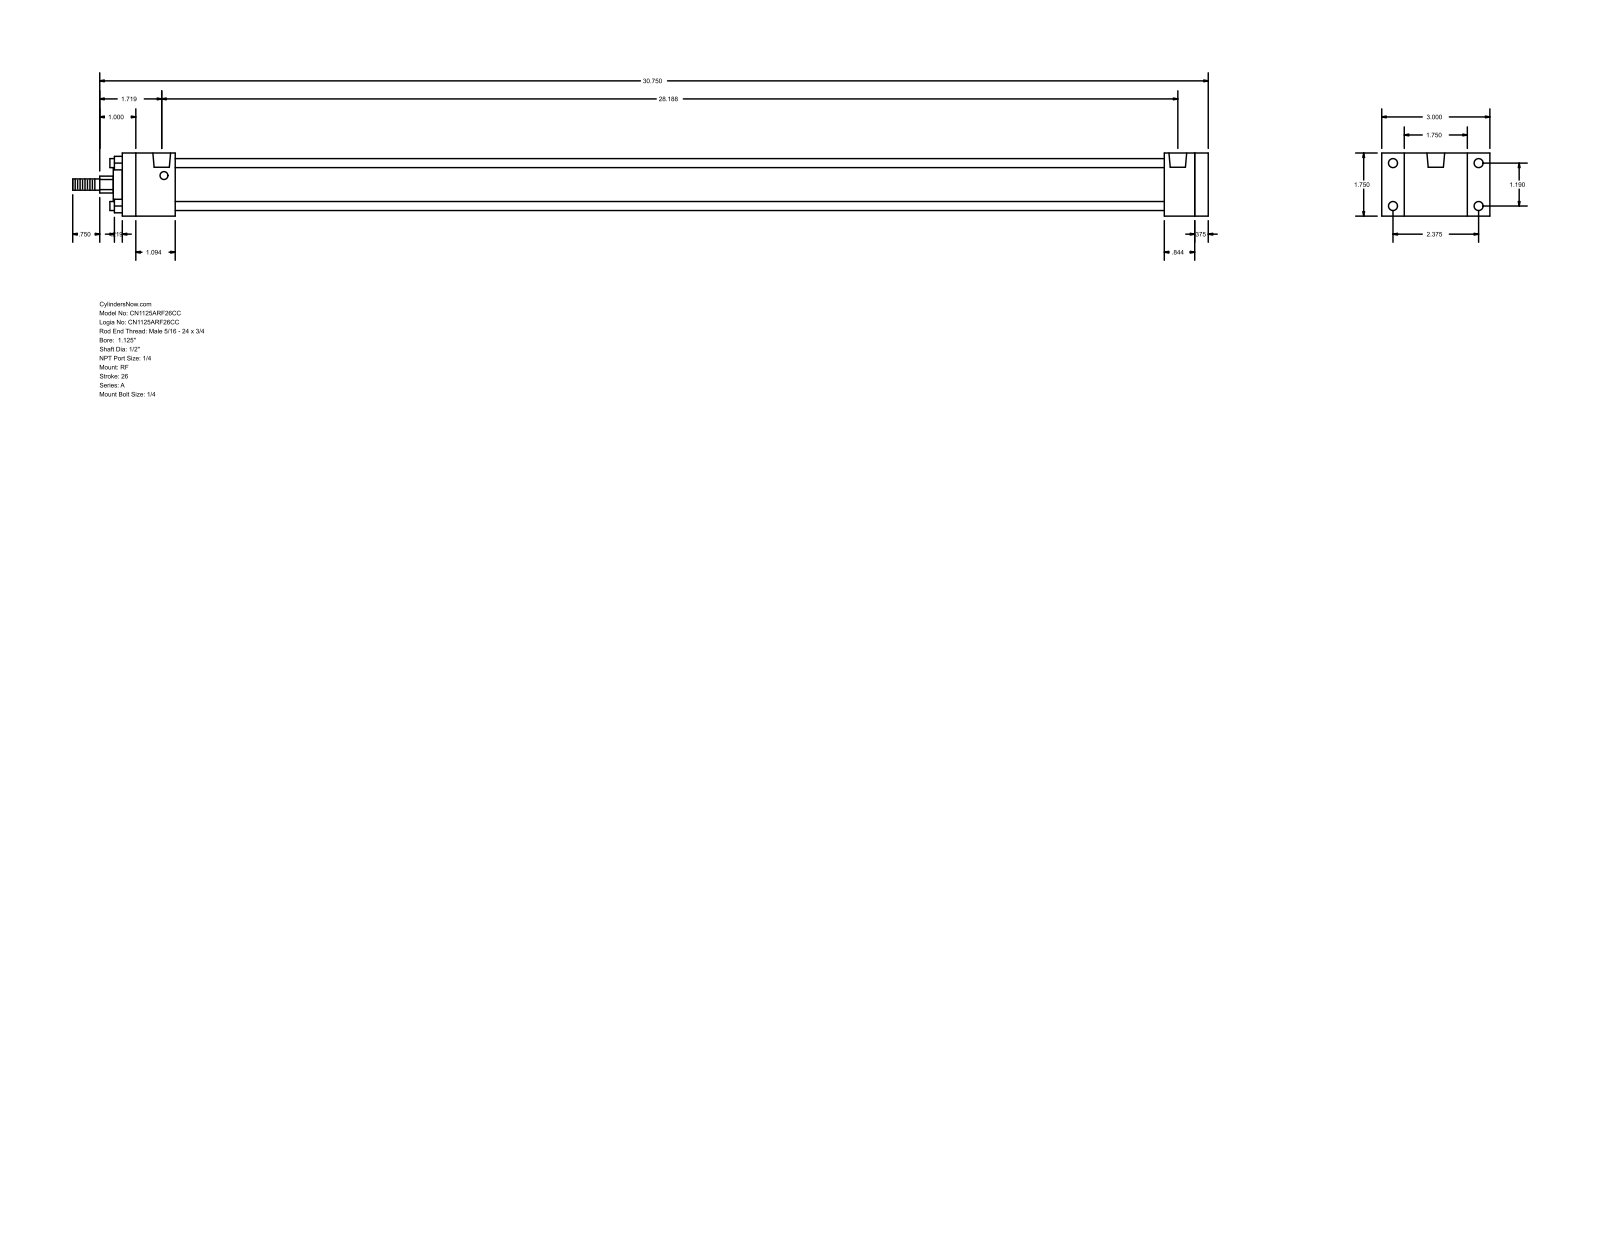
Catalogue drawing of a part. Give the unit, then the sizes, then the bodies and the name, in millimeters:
Units: millimetres
Overall size (bounding box): 800.1 × 76.2 × 44.45
Round holes (diameter × count): ⌀5.56 ×4, ⌀6.35 ×4, ⌀12.49 ×2
Round bosses / shafts (diameter × count): ⌀6.35 ×4, ⌀31.88 ×1, ⌀23.81 ×1, ⌀12.7 ×1, ⌀7.94 ×1
Partial cylindrical surfaces — rounded edges, fillets, slot ends (radius × count): R5.94 ×1
Main face-to-face distances: 44.46, 9.53, 765.17, 755.64, 37.3, 734.21, 696.91, 718.34, 727.87, 21.43
Hole centre spacings: 30.22, 60.32, 67.47, 712.79, 1.58, 1.59, 714.37, 714.38
Bodies: 0 solids, 92 faces (64 planar, 28 cylindrical, 0 other)
Part name (STEP PRODUCT): A_RF__0112_0.5
STEP written by: GSSL Pune (CONFIG_CONTROL_DESIGN)
